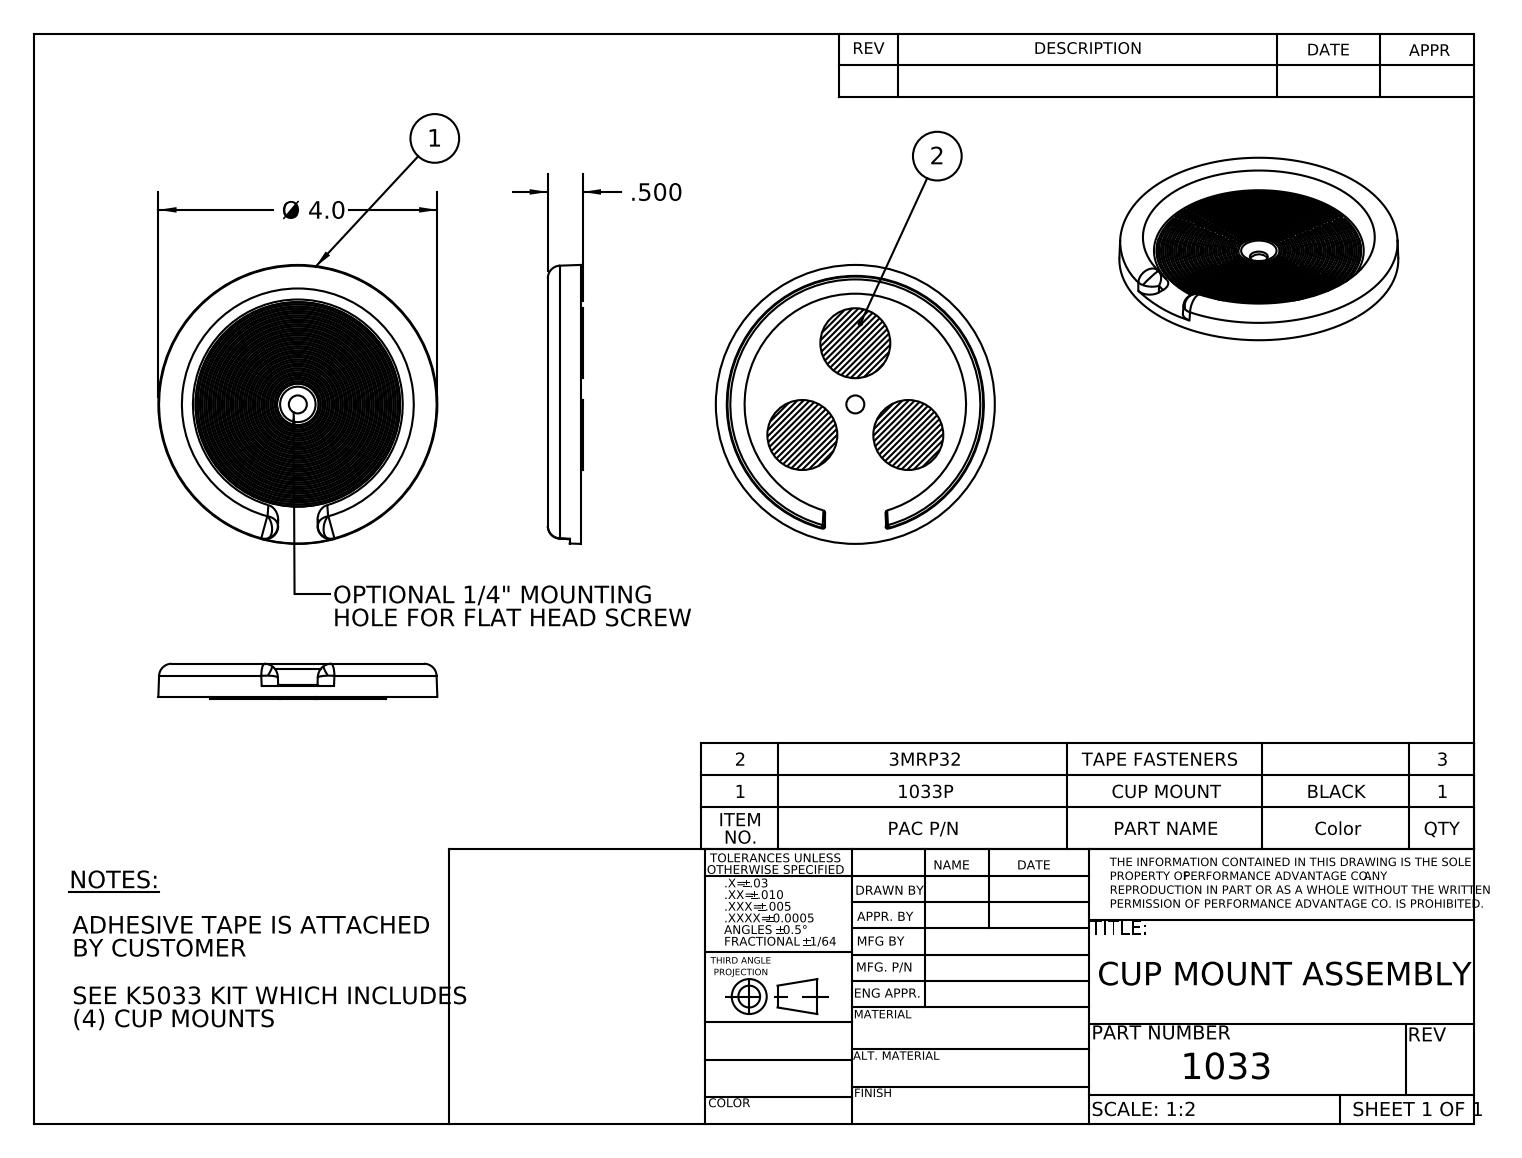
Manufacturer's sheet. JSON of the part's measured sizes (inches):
{"part_name": "1033; 1033P; RP32 (SET)", "step_written_by": "SolidWorks 2010 (CONFIG_CONTROL_DESIGN)", "units": "inches", "bodies": {"solids": 4, "faces": 188, "planar": 31, "cylindrical": 8, "other": 149}, "overall_size": [3.989, 3.989, 0.5], "volume_in3": 2.751, "surface_area_in2": 42.61, "round_holes": [[0.257, 1]], "round_bosses_or_shafts": [[1, 3]], "face_to_face_distances": [0.156, 0.187, 0.031]}
